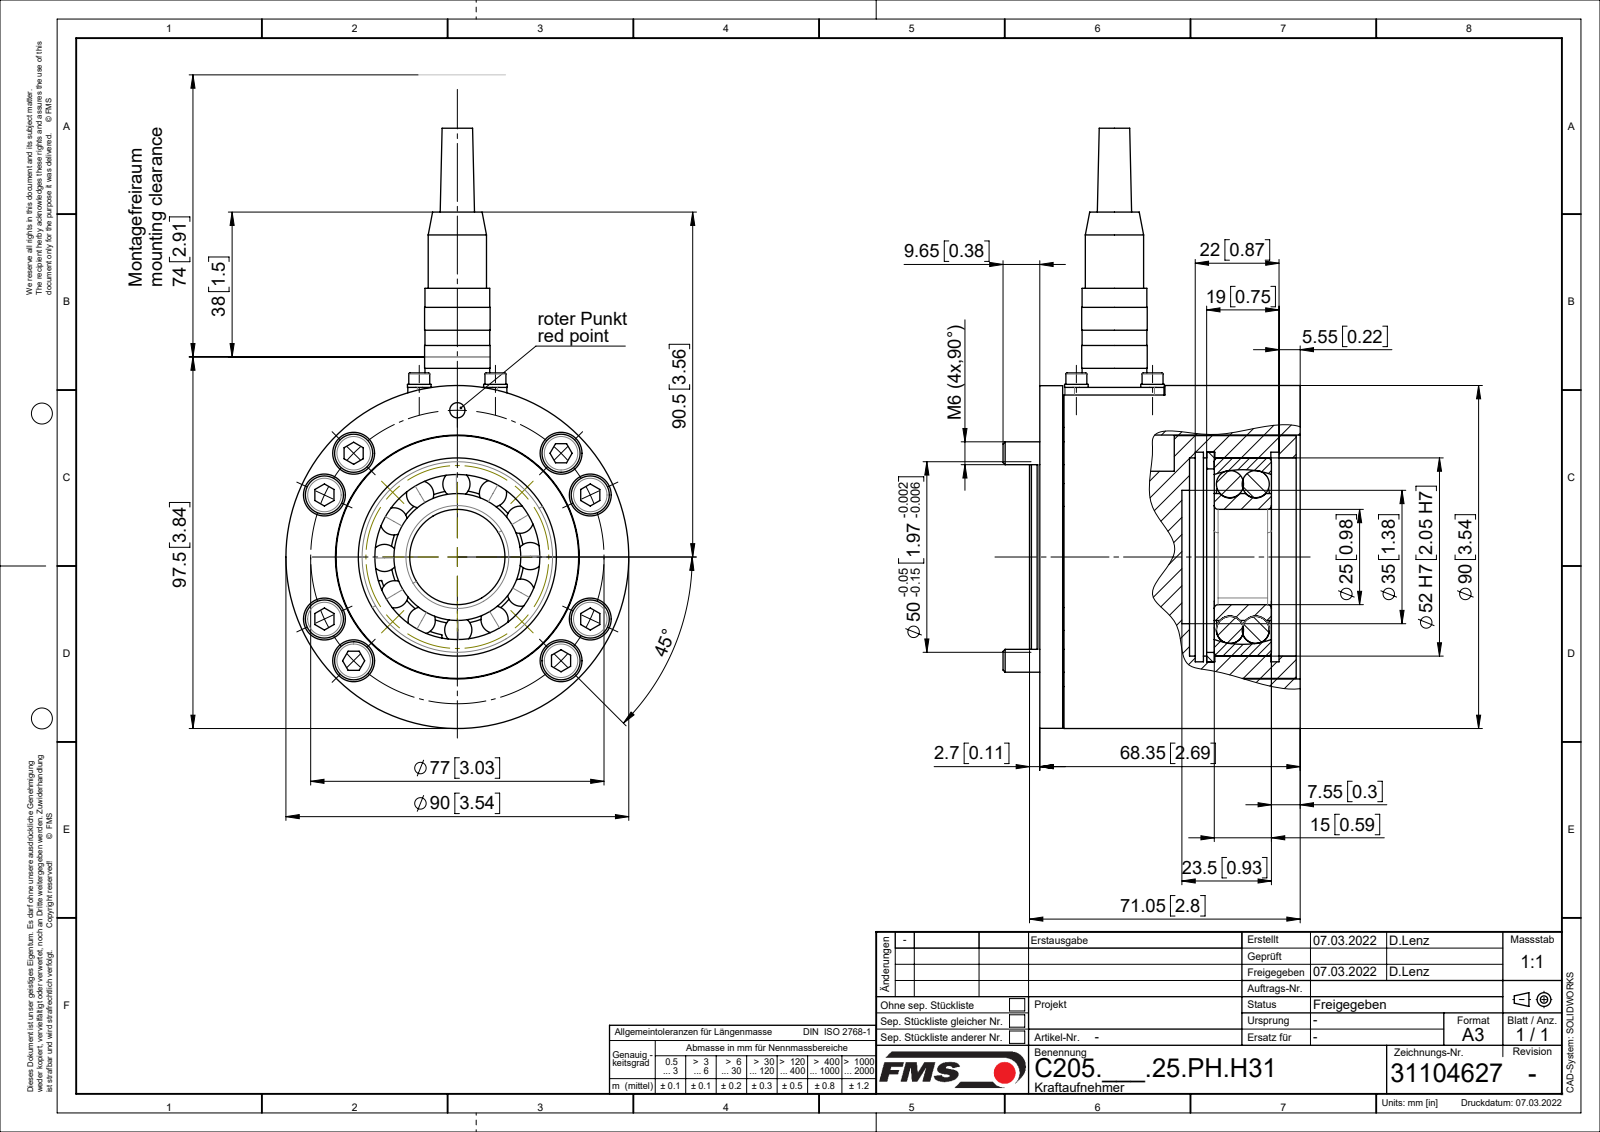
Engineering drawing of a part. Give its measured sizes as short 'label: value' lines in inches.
name: 31104488_01; Zyl-Schr DIN912_M3x6; Zyl-Schr DIN912_M6x40; 31104486_stp_nach_Vergueten (+8 more)
written by: SolidWorks 2018 (CONFIG_CONTROL_DESIGN)
unit: in
bodies: 48 solids, 630 faces (206 planar, 260 cylindrical, 164 other)
size: 6.201 × 3.543 × 3.071
volume: 18.75 in³; area: 191.3 in²
holes: 8× ⌀0.256, 8× ⌀0.433, 6× ⌀0.098, 4× ⌀0.122, 4× ⌀0.126, 4× ⌀0.197, 4× ⌀0.276, 2× ⌀0.157, 1× ⌀0.402, 1× ⌀0.472, 1× ⌀0.591, 1× ⌀0.709
bosses: 8× ⌀0.394, 8× ⌀0.236, 5× ⌀0.059, 4× ⌀0.244, 4× ⌀0.217, 4× ⌀0.118, 1× ⌀3.543, 1× ⌀3.539
rounds: 4× R0.004, 4× R0.098, 2× R0.167, 2× R0.197, 1× R0.819, 1× R0.949
face distances: 0.236, 0.13, 0.106, 0.079, 0.256, 1.26, 1.301, 1.496, 1.181, 1.154
hole spacings: 0.787, 1.516, 0.526, 0.557, 1.515, 1.739, 2.143, 2.483
